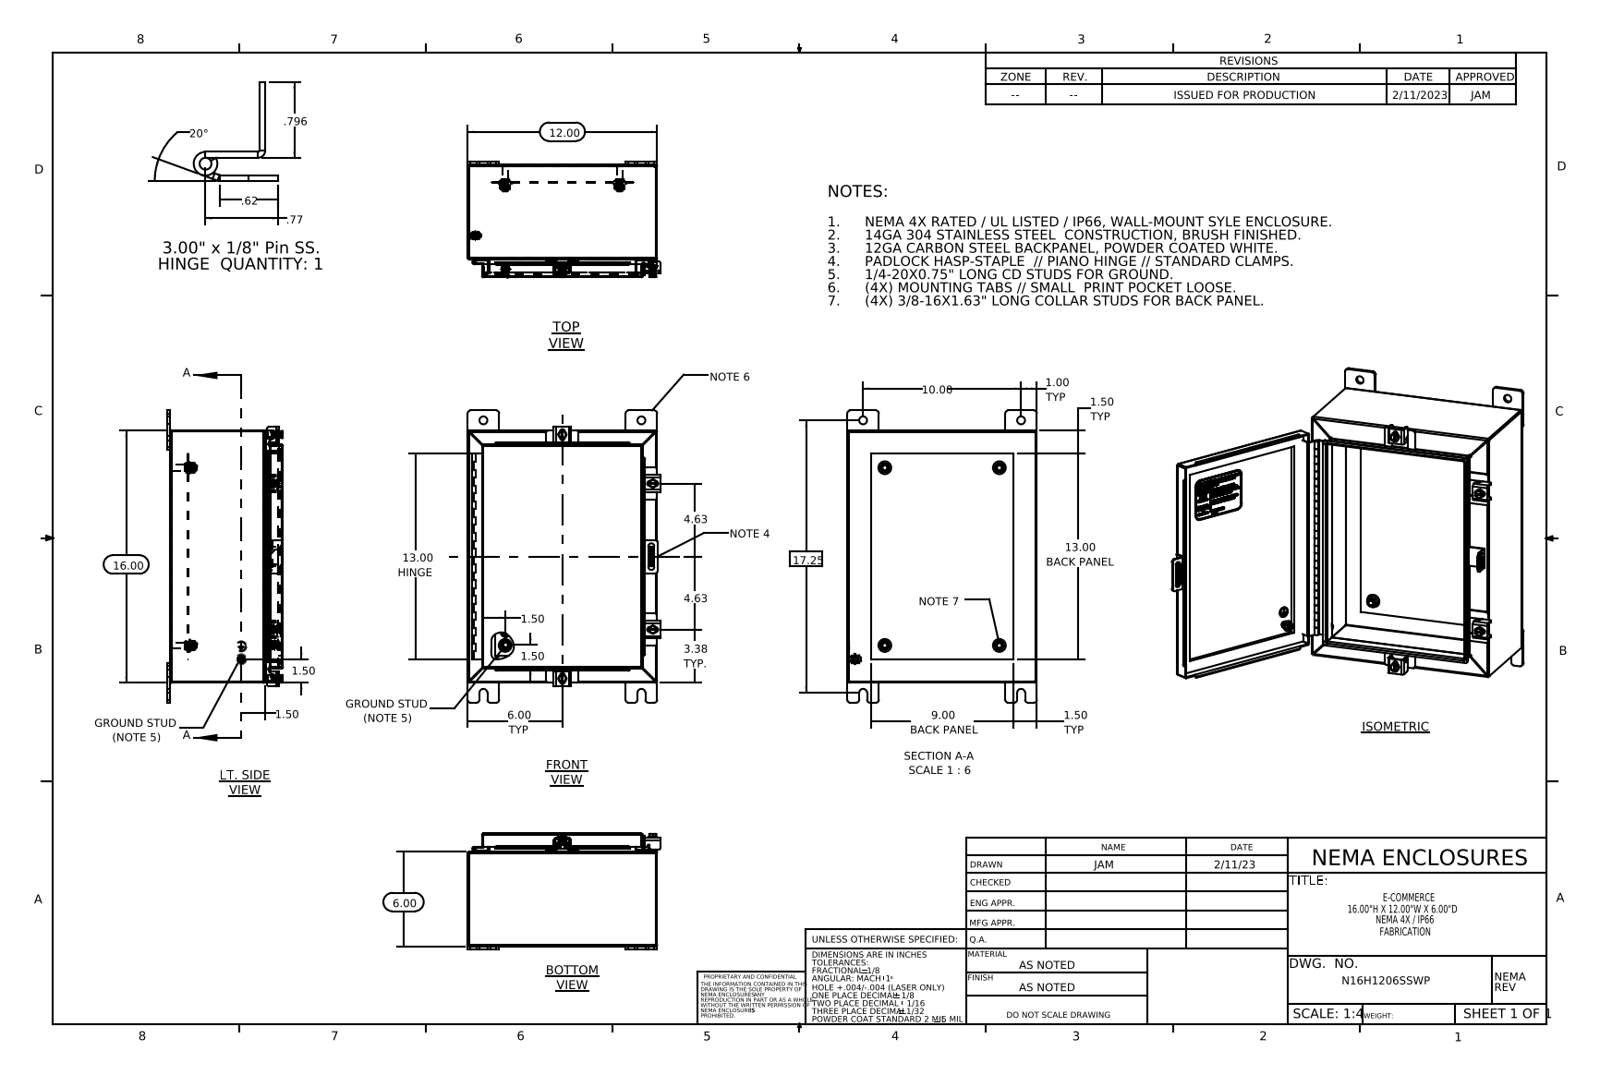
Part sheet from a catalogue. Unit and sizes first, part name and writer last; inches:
Units: inches
Overall size (bounding box): 18.5 × 12.211 × 7.389
Round holes (diameter × count): ⌀0.5 ×8, ⌀0.213 ×4, ⌀0.26 ×4, ⌀0.125 ×2, ⌀0.125 ×1
Round bosses / shafts (diameter × count): ⌀0.25 ×5, ⌀0.625 ×4, ⌀0.5 ×4, ⌀0.399 ×4, ⌀0.375 ×4, ⌀0.33 ×4
Partial cylindrical surfaces — rounded edges, fillets, slot ends (radius × count): R0.19 ×24, R0.013 ×23, R0.06 ×22, R0.088 ×21, R0.125 ×10, R0.12 ×8, R0.141 ×8, R0.05 ×7
Main face-to-face distances: 0.075, 7.126, 11.925, 7.201, 7.051, 15.925, 5.925, 1.201, 1, 1.075
Hole centre spacings: 13.834, 2.225, 2.327, 3.3, 4.189, 4.19, 5.012, 5.08
Volume: 81.37 in³ · Surface area: 2 072 in²
Bodies: 37 solids, 1267 faces (680 planar, 507 cylindrical, 80 other)
Part name (STEP PRODUCT): N16H1206SSWP Clamp Bracket; N16H1206SSWP; N16H1206SSWP 22101002; N16H1206SSWP Backpanel (+8 more)
STEP written by: SolidWorks 2013 (CONFIG_CONTROL_DESIGN)
